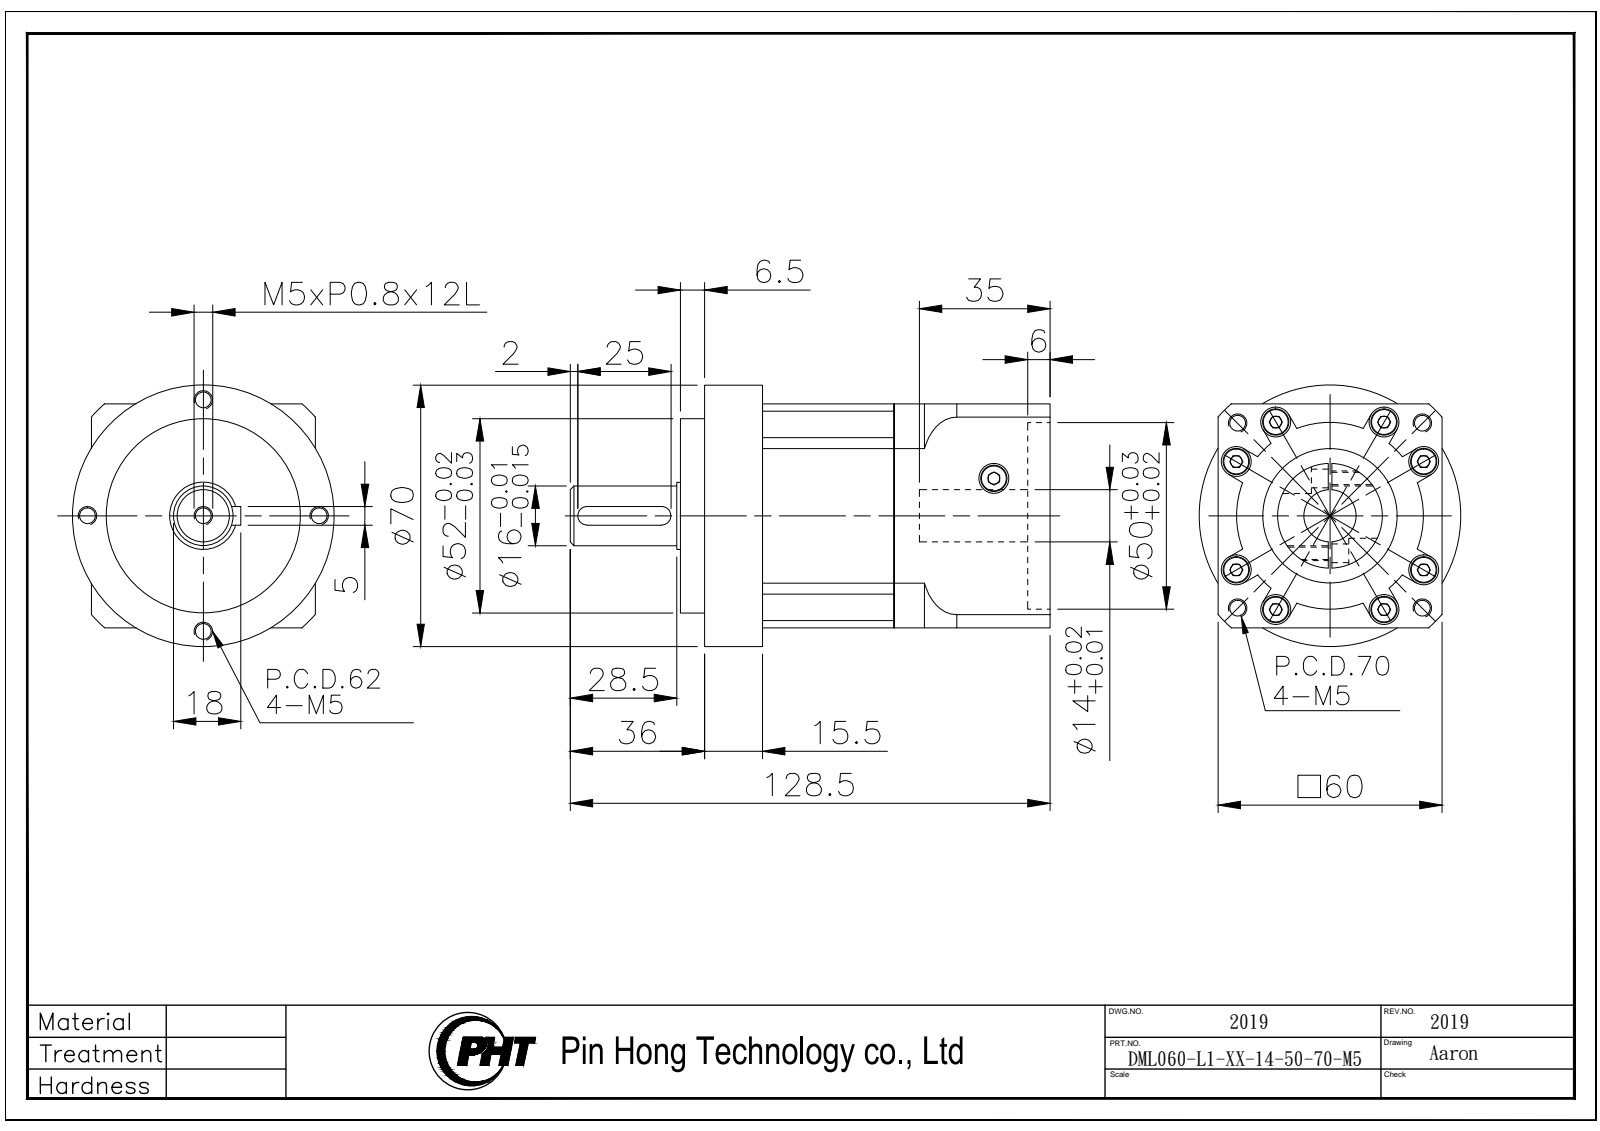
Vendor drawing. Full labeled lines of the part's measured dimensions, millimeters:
Part name (STEP PRODUCT): DML060-L1-XX-14-50-70-M5_2019
STEP written by: SolidWorks 2016 (AUTOMOTIVE_DESIGN)
Units: millimetres
Bodies: 3 solids, 284 faces (124 planar, 120 cylindrical, 40 other)
Overall size (bounding box): 128.5 × 70 × 70
Volume: 296 792 mm³ · Surface area: 62 364 mm²
Round holes (diameter × count): ⌀8 ×10, ⌀4.2 ×9, ⌀4.5 ×8, ⌀14 ×1, ⌀36 ×1
Round bosses / shafts (diameter × count): ⌀7 ×8, ⌀70 ×1, ⌀52 ×1, ⌀28 ×1, ⌀18 ×1, ⌀16 ×1
Partial cylindrical surfaces — rounded edges, fillets, slot ends (radius × count): R5 ×4, R2.5 ×2, R25 ×1, R40 ×1
Main face-to-face distances: 60, 35.35, 57.35, 22, 50.85, 15.5, 6.5, 77, 41.65, 92.5
Hole centre spacings: 29, 10.26, 15.65, 25.53, 30.05, 39.25, 41.01, 50.9
